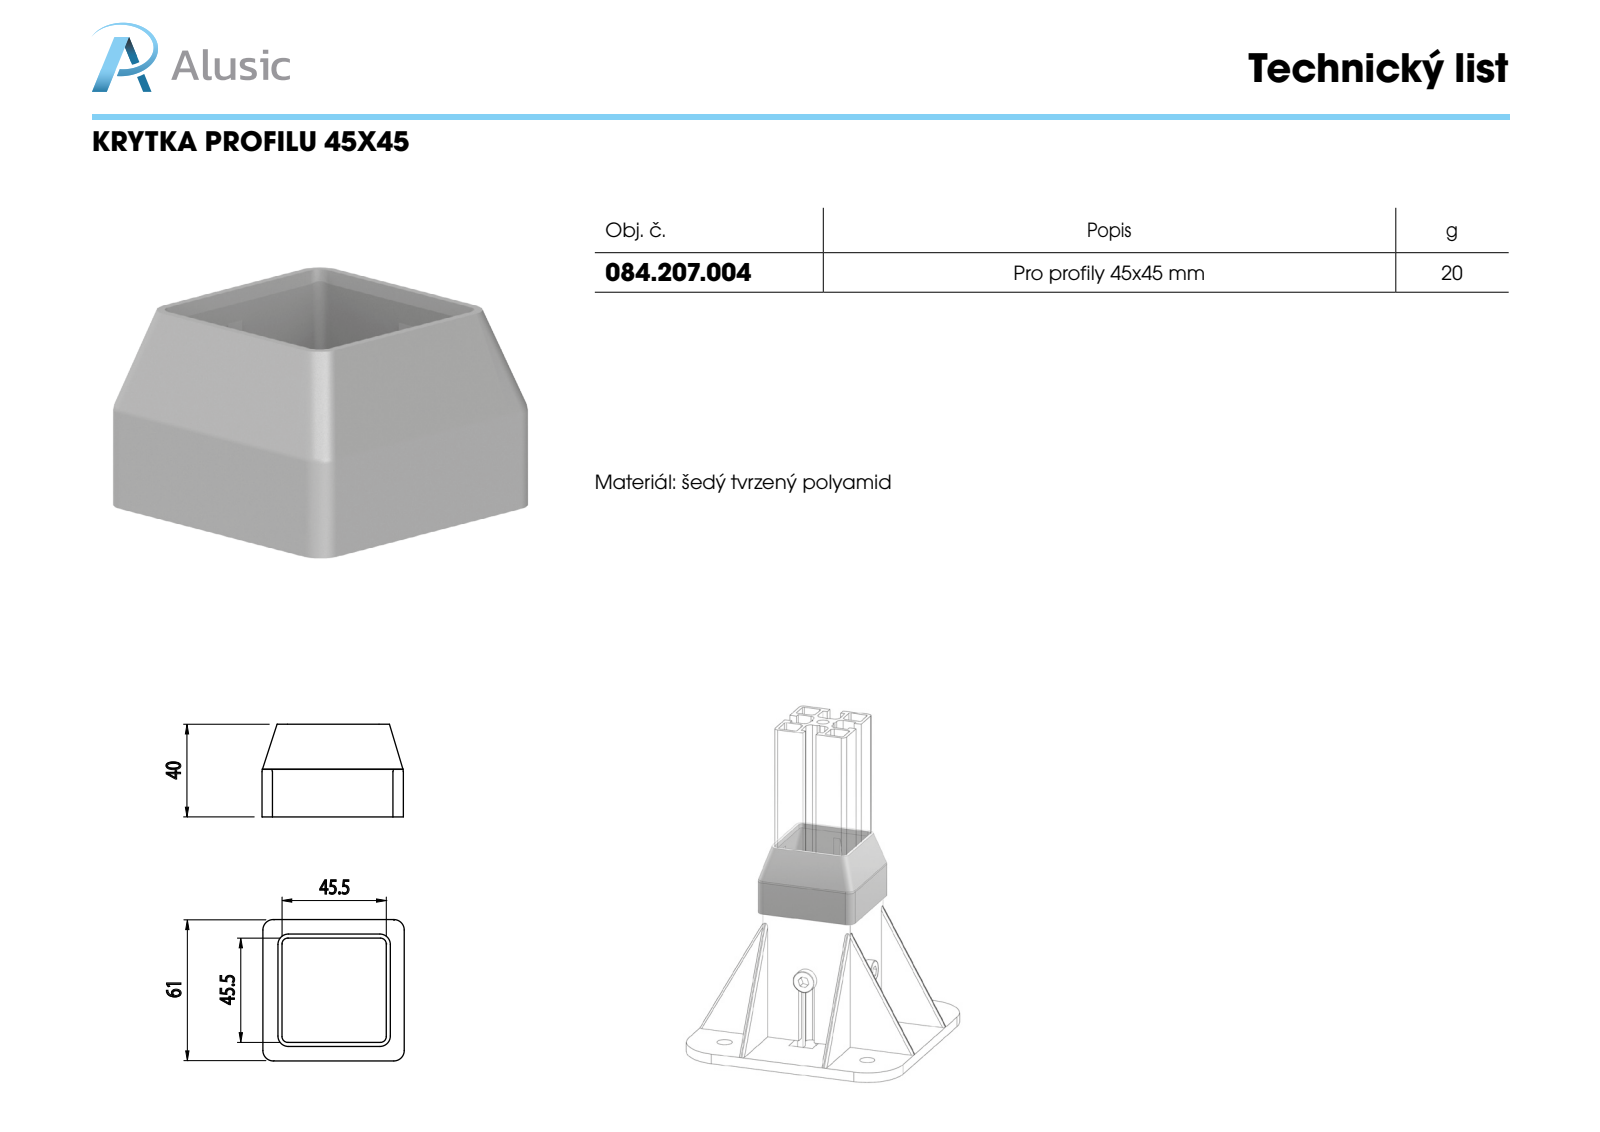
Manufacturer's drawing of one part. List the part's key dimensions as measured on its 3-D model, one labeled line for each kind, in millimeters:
Part name (STEP PRODUCT): 084.207.004
STEP written by: SolidWorks 2011 (CONFIG_CONTROL_DESIGN)
Units: millimetres
Bodies: 1 solid, 56 faces (32 planar, 12 cylindrical, 12 other)
Overall size (bounding box): 61 × 61 × 40
Volume: 20 122 mm³ · Surface area: 18 786 mm²
Partial cylindrical surfaces — rounded edges, fillets, slot ends (radius × count): R2 ×4, R2.5 ×4, R4.5 ×4
Main face-to-face distances: 2.5, 58.5, 56, 61, 26, 40, 4, 8, 53, 5.5
